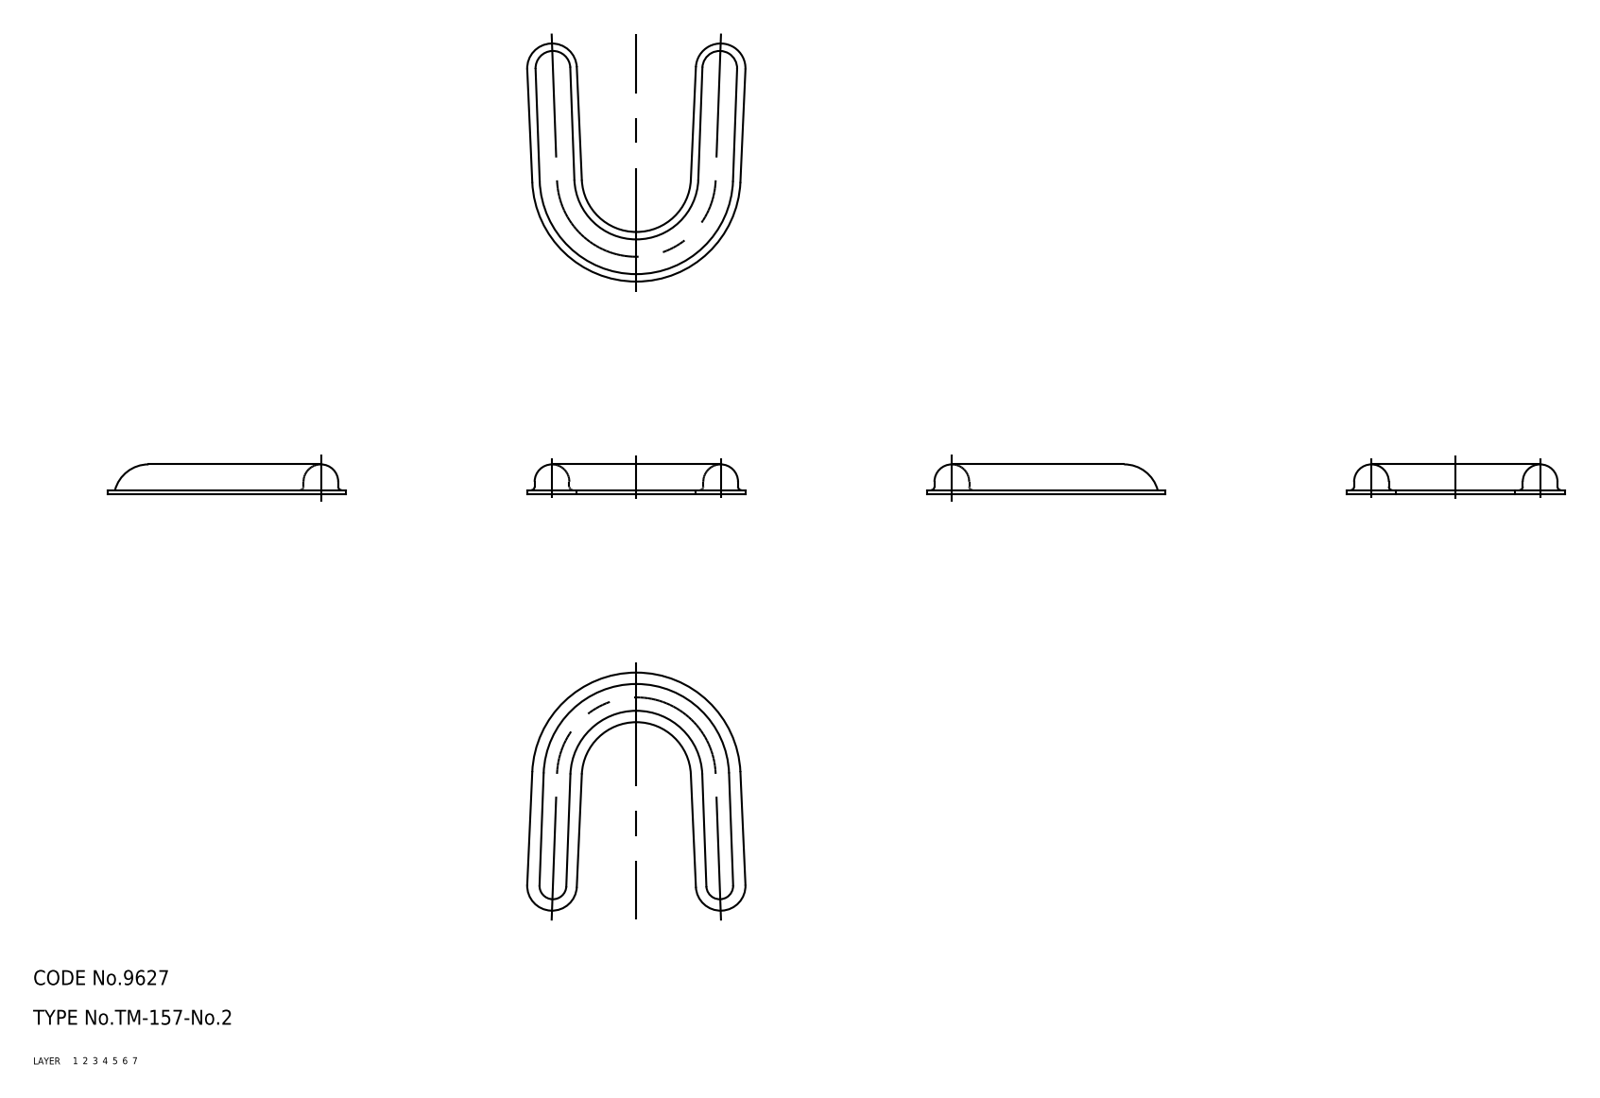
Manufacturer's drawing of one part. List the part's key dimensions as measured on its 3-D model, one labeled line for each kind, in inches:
Part name (STEP PRODUCT): holder
STEP written by: CADfix (AUTOMOTIVE_DESIGN)
Units: inches
Bodies: 1 solid, 70 faces (0 planar, 0 cylindrical, 70 other)
Overall size (bounding box): 1.89 × 1.718 × 0.236
Volume: 0.088 in³ · Surface area: 5.706 in²
